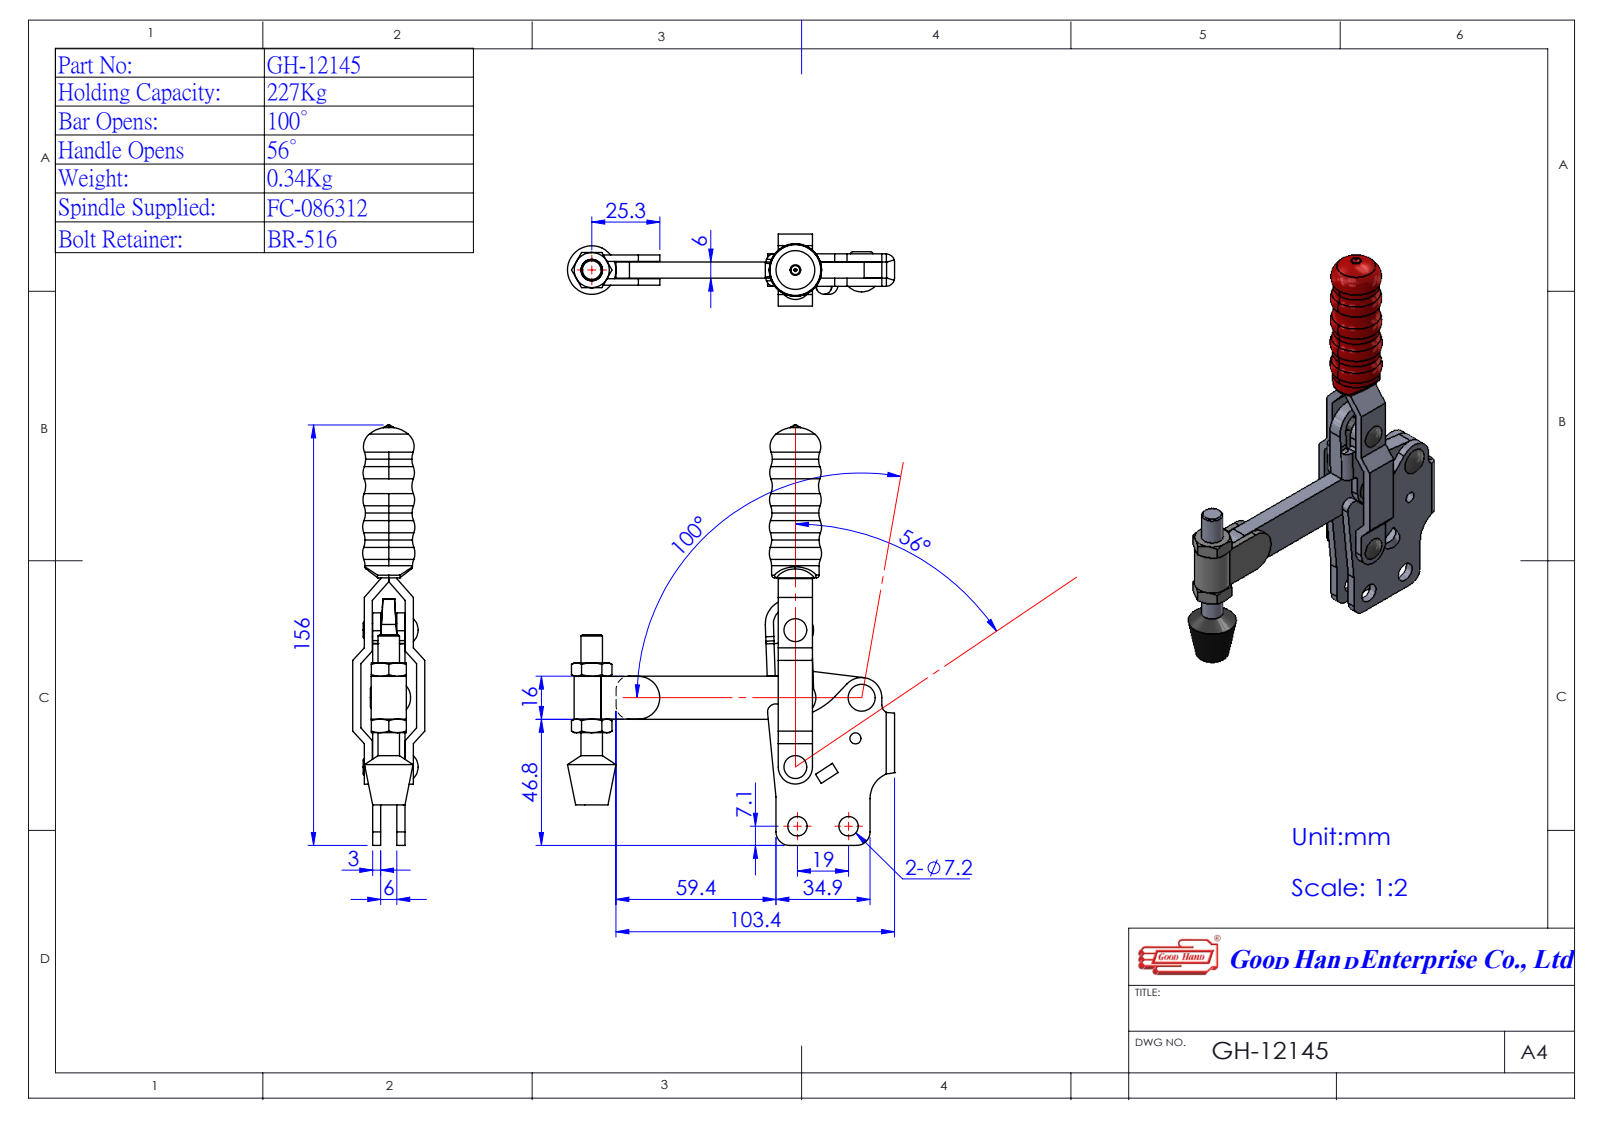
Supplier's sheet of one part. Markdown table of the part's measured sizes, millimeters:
| quantity | value |
| --- | --- |
| part name | 11214008-1^GH-12145(簡化); Group5^GH-12145(簡化); Group4^GH-12135(簡化); Group1^GH-12130(簡化) (+2 more) |
| STEP written by | SolidWorks 2016 (AUTOMOTIVE_DESIGN) |
| units | millimeters |
| bodies | 5 solids, 311 faces (127 planar, 98 cylindrical, 86 other) |
| overall size | 156.16 × 121.41 × 26.7 |
| volume | 55 511 mm³ |
| surface area | 31 889 mm² |
| round holes (diameter × count) | 4 × 5, 7.2 × 2 |
| round bosses / shafts (diameter × count) | 17.61 × 1, 7.93 × 1 |
| partial cylindrical surfaces (radius × count) | 7.5 × 4, 0.1 × 2, 1 × 2, 2 × 2, 2.42 × 2, 3 × 2, 3.1 × 2, 5 × 2 |
| main face-to-face distances | 3, 9, 6, 12, 12.1, 3.1, 7.35, 16.35, 19.45, 4.25 |
| hole center spacings | 15.27, 19, 22.01, 23.4, 24.69, 25.13, 25.73, 25.95 |
